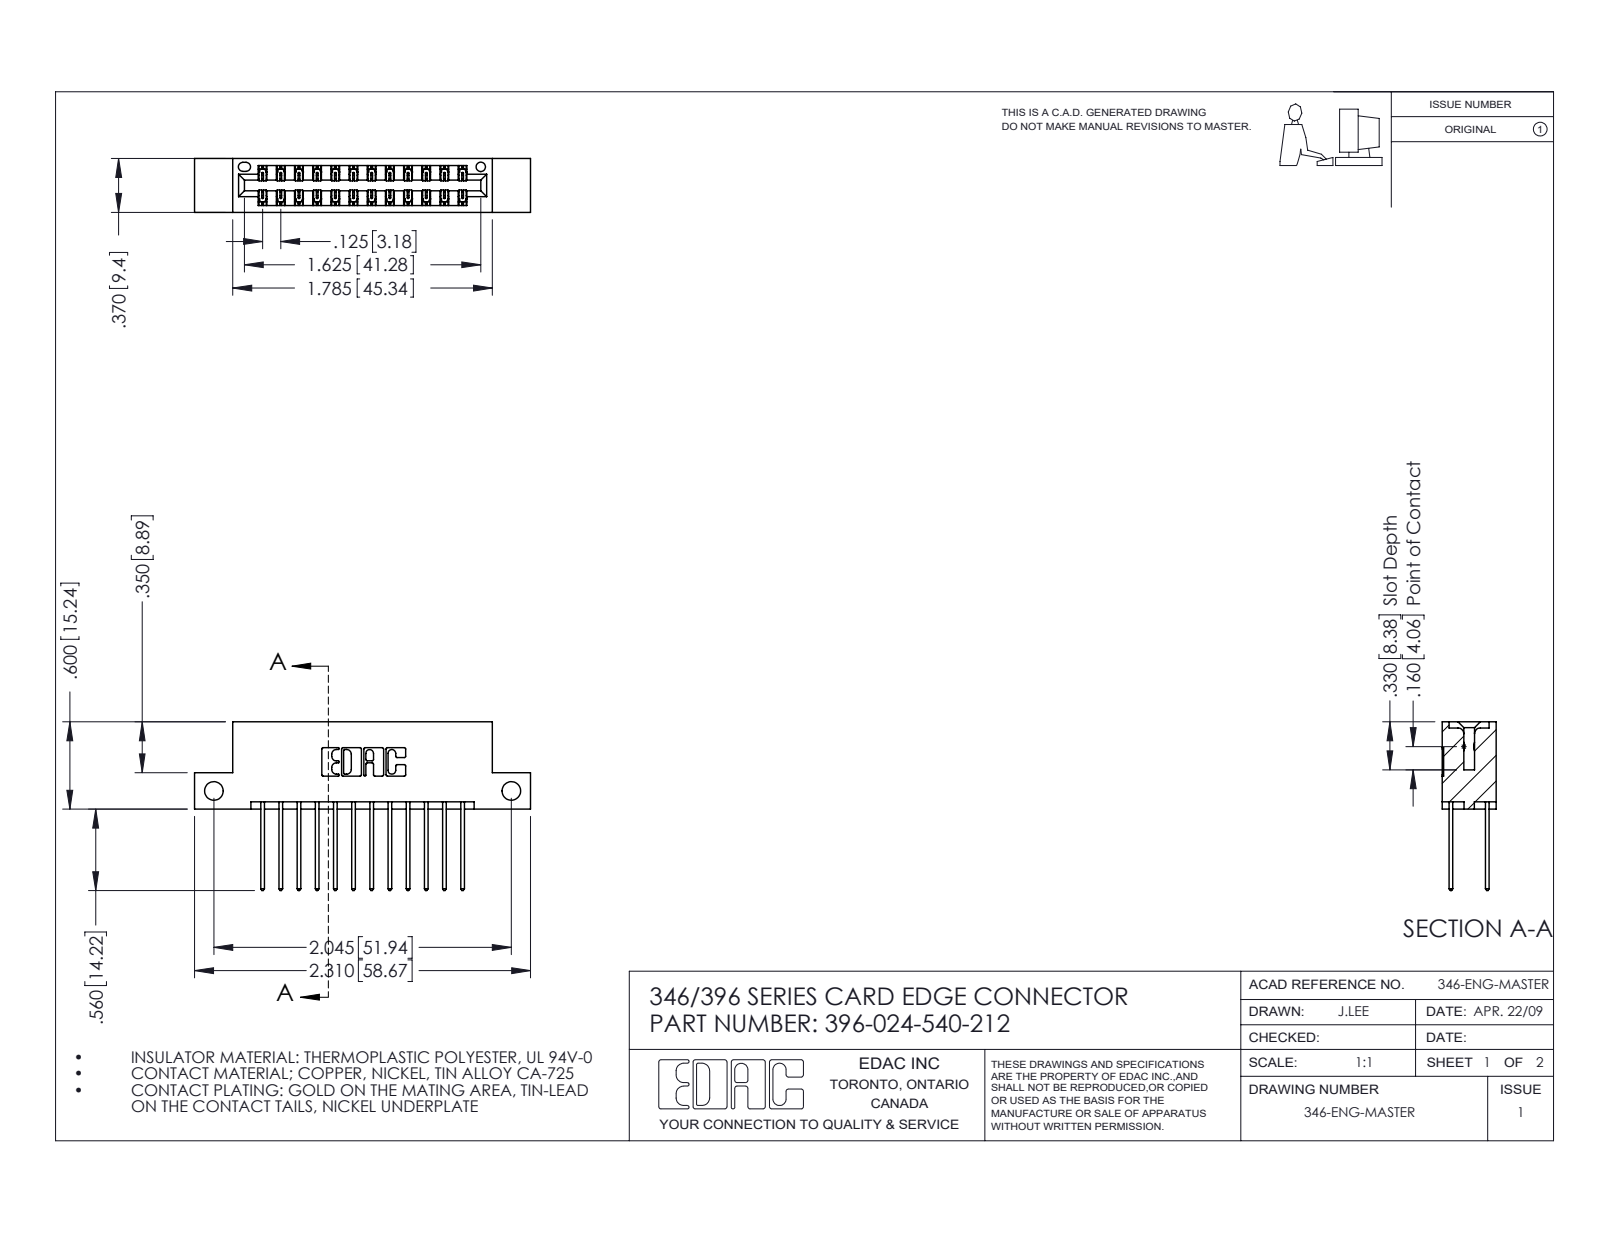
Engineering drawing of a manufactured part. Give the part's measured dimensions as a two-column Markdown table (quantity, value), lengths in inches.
| quantity | value |
| --- | --- |
| part name | 396-024-540-212; 346 Part_Flush Mounting Lugs - Side Mount; 345-292-001_345-293-140 |
| STEP written by | SolidWorks 2016 (CONFIG_CONTROL_DESIGN) |
| units | inches |
| bodies | 25 solids, 1370 faces (916 planar, 454 cylindrical, 0 other) |
| overall size | 2.31 × 1.16 × 0.37 |
| volume | 0.335 in³ |
| surface area | 11.42 in² |
| round holes (diameter × count) | 0.128 × 2, 0.064 × 1 |
| partial cylindrical surfaces (radius × count) | 0.006 × 36, 0.01 × 24, 0.01 × 22, 0.007 × 6, 0.031 × 6, 0.026 × 3, 0.014 × 2, 0.022 × 2 |
| main face-to-face distances | 0.25, 0.048, 0.322, 0.37, 0.072, 0.298, 0.025, 0.275, 0.148, 0.222 |
| hole center spacings | 2.045 |
